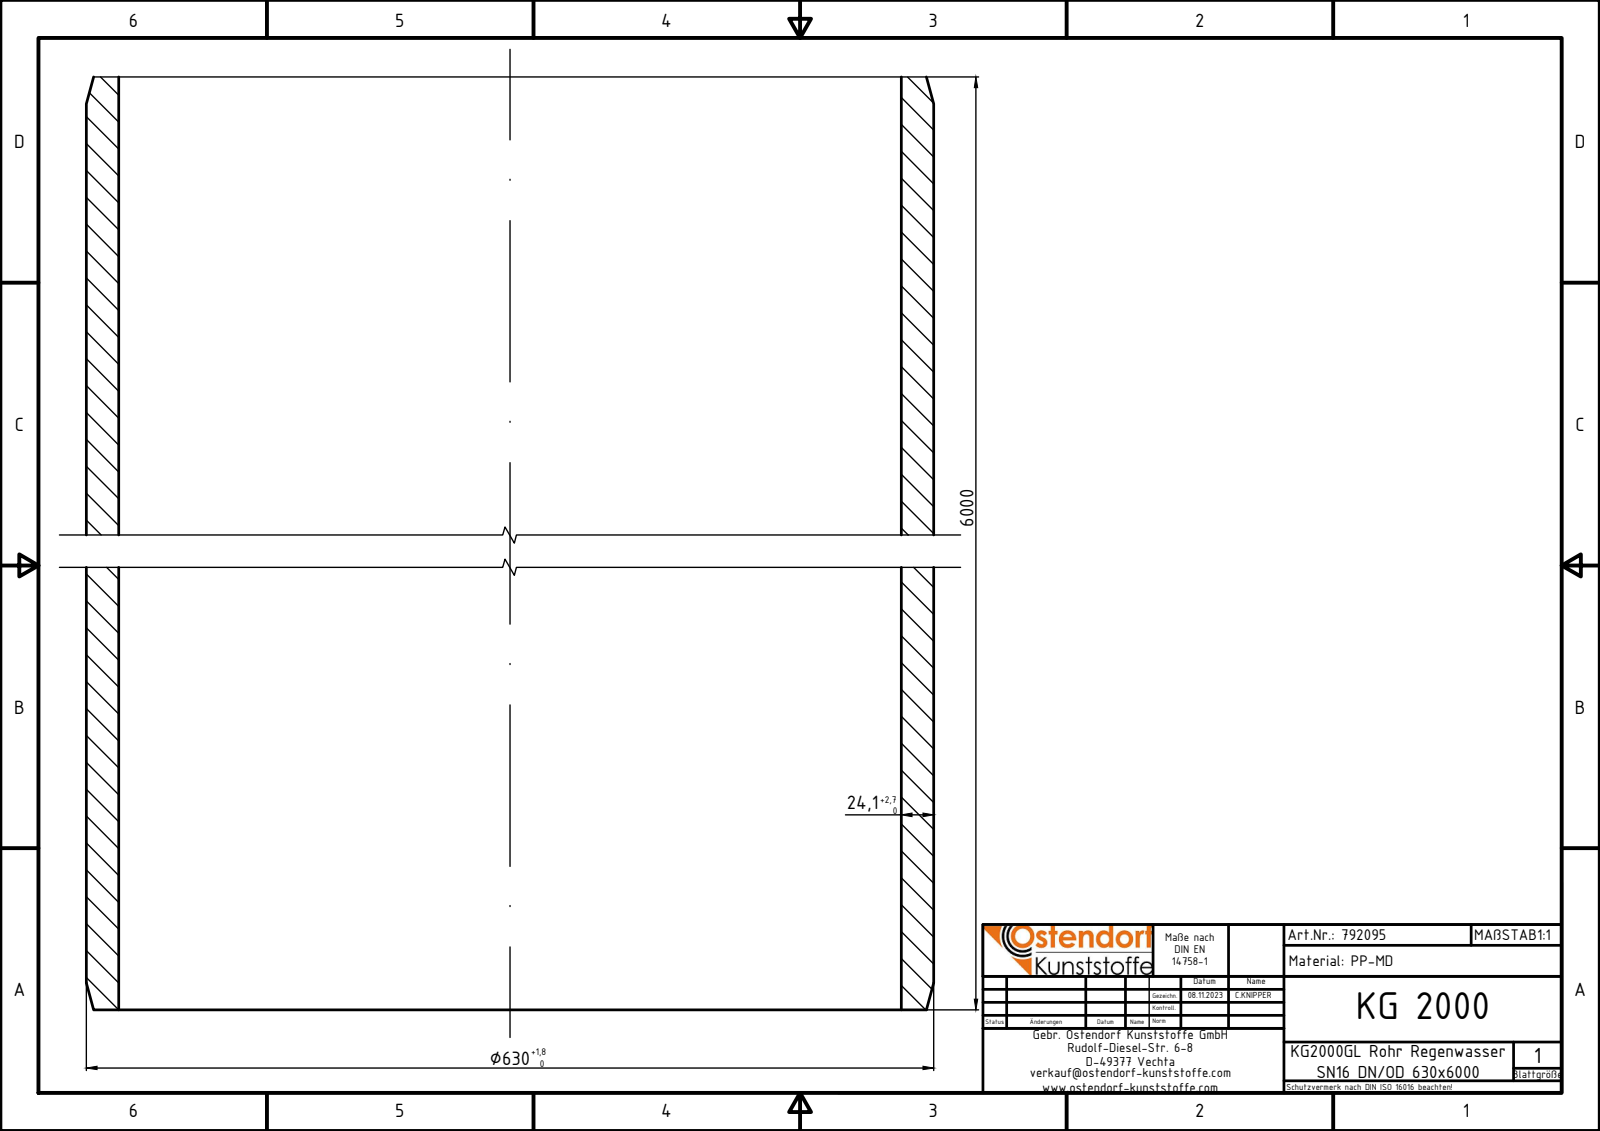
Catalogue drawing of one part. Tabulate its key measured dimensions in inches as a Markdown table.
| quantity | value |
| --- | --- |
| part name | 792095z |
| STEP written by | Autodesk Inventor 2024 (AUTOMOTIVE_DESIGN) |
| units | inches |
| bodies | 1 solid, 6 faces (2 planar, 2 cylindrical, 2 other) |
| overall size | 236.22 × 24.803 × 24.803 |
| volume | 16 780 in³ |
| surface area | 35 510 in² |
| round holes (diameter × count) | 22.906 × 1 |
| round bosses / shafts (diameter × count) | 24.803 × 1 |
| main face-to-face distances | 236.22 |
